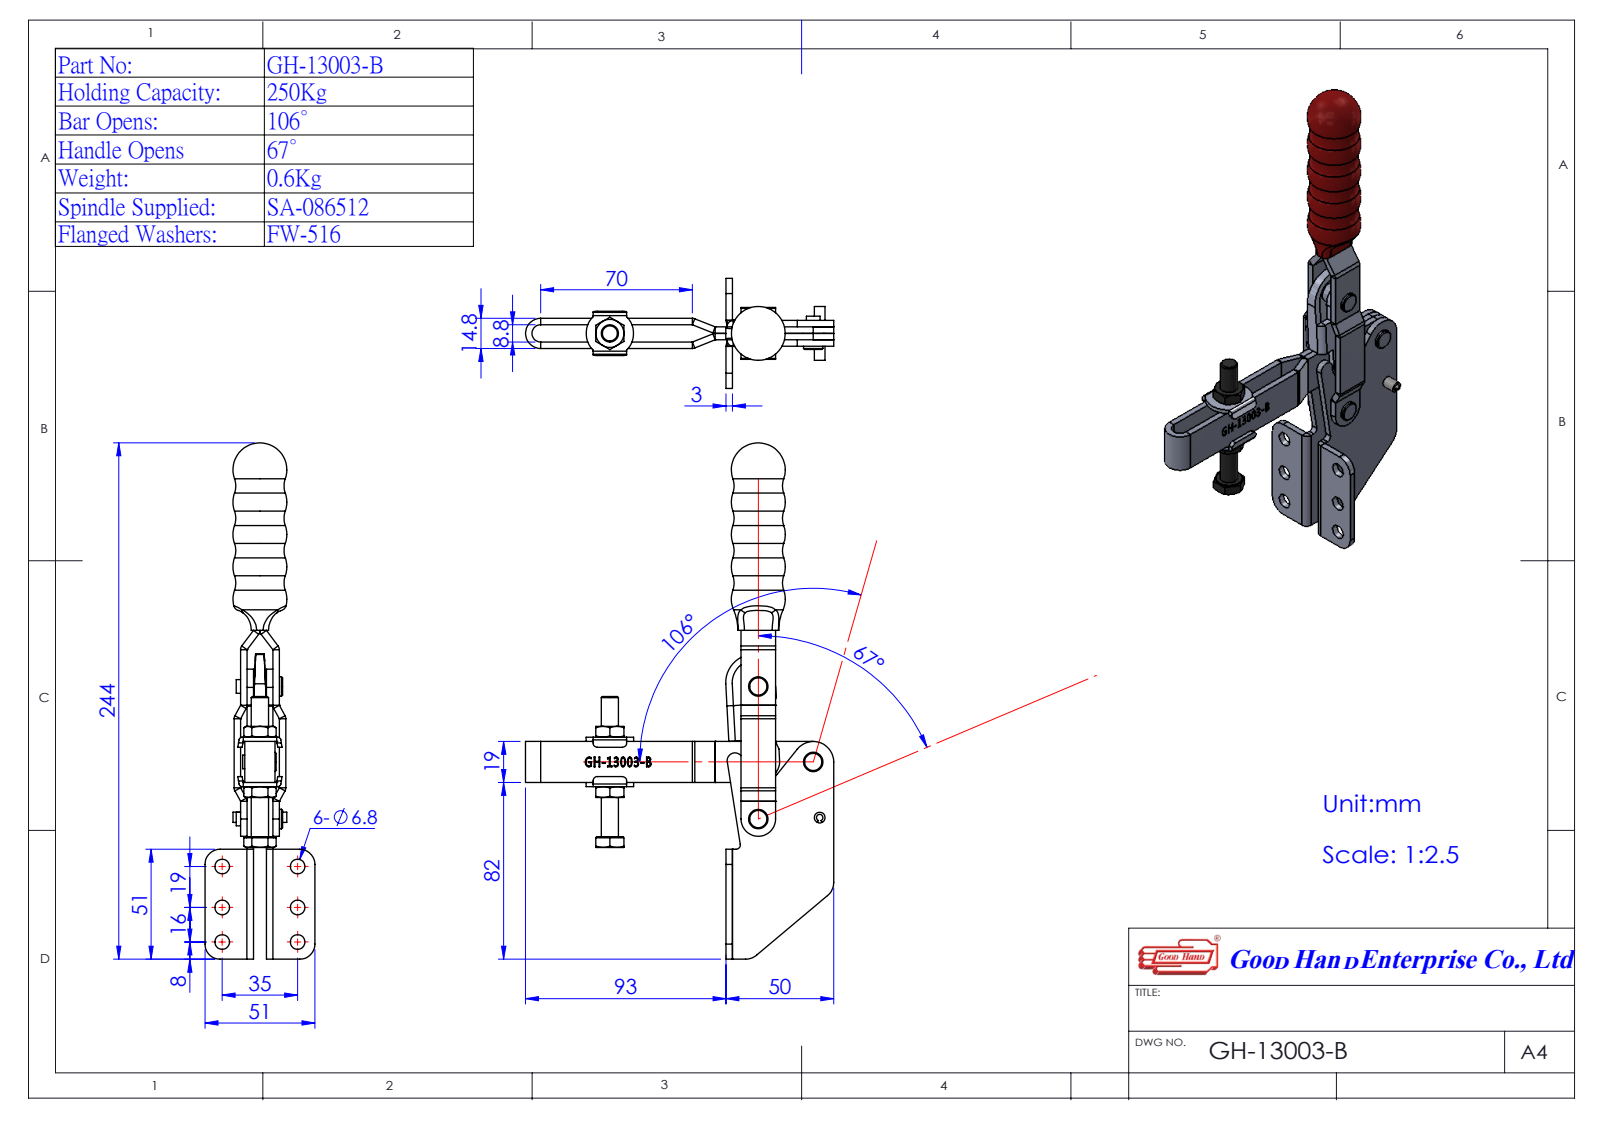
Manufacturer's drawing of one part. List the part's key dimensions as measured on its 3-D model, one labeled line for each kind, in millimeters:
Part name (STEP PRODUCT): 零件5^GH-13003-B(簡化)-1; Group5^GH-13003-B(簡化)-1; GH-13003-B(簡化)-1; Group1^GH-13003-B(簡化)-1 (+3 more)
STEP written by: SolidWorks 2016 (AUTOMOTIVE_DESIGN)
Units: millimetres
Bodies: 8 solids, 358 faces (162 planar, 126 cylindrical, 70 other)
Overall size (bounding box): 244 × 143 × 51
Volume: 113 661 mm³ · Surface area: 60 028 mm²
Round holes (diameter × count): ⌀6.8 ×7, ⌀5 ×4, ⌀8 ×1, ⌀8.3 ×1
Round bosses / shafts (diameter × count): ⌀9 ×4, ⌀7.5 ×3, ⌀6.27 ×2, ⌀12.5 ×1, ⌀5 ×1
Partial cylindrical surfaces — rounded edges, fillets, slot ends (radius × count): R1.2 ×4, R3.6 ×4, R7 ×4, R8 ×3, R2 ×2, R11.04 ×2, R3.65 ×1, R4.4 ×1
Main face-to-face distances: 3, 9, 6, 12, 1.4, 4.4, 7.4, 10.4, 13.4, 1.6
Hole centre spacings: 35, 16, 19, 38.48, 39.82, 49.5, 23.67, 26.56
